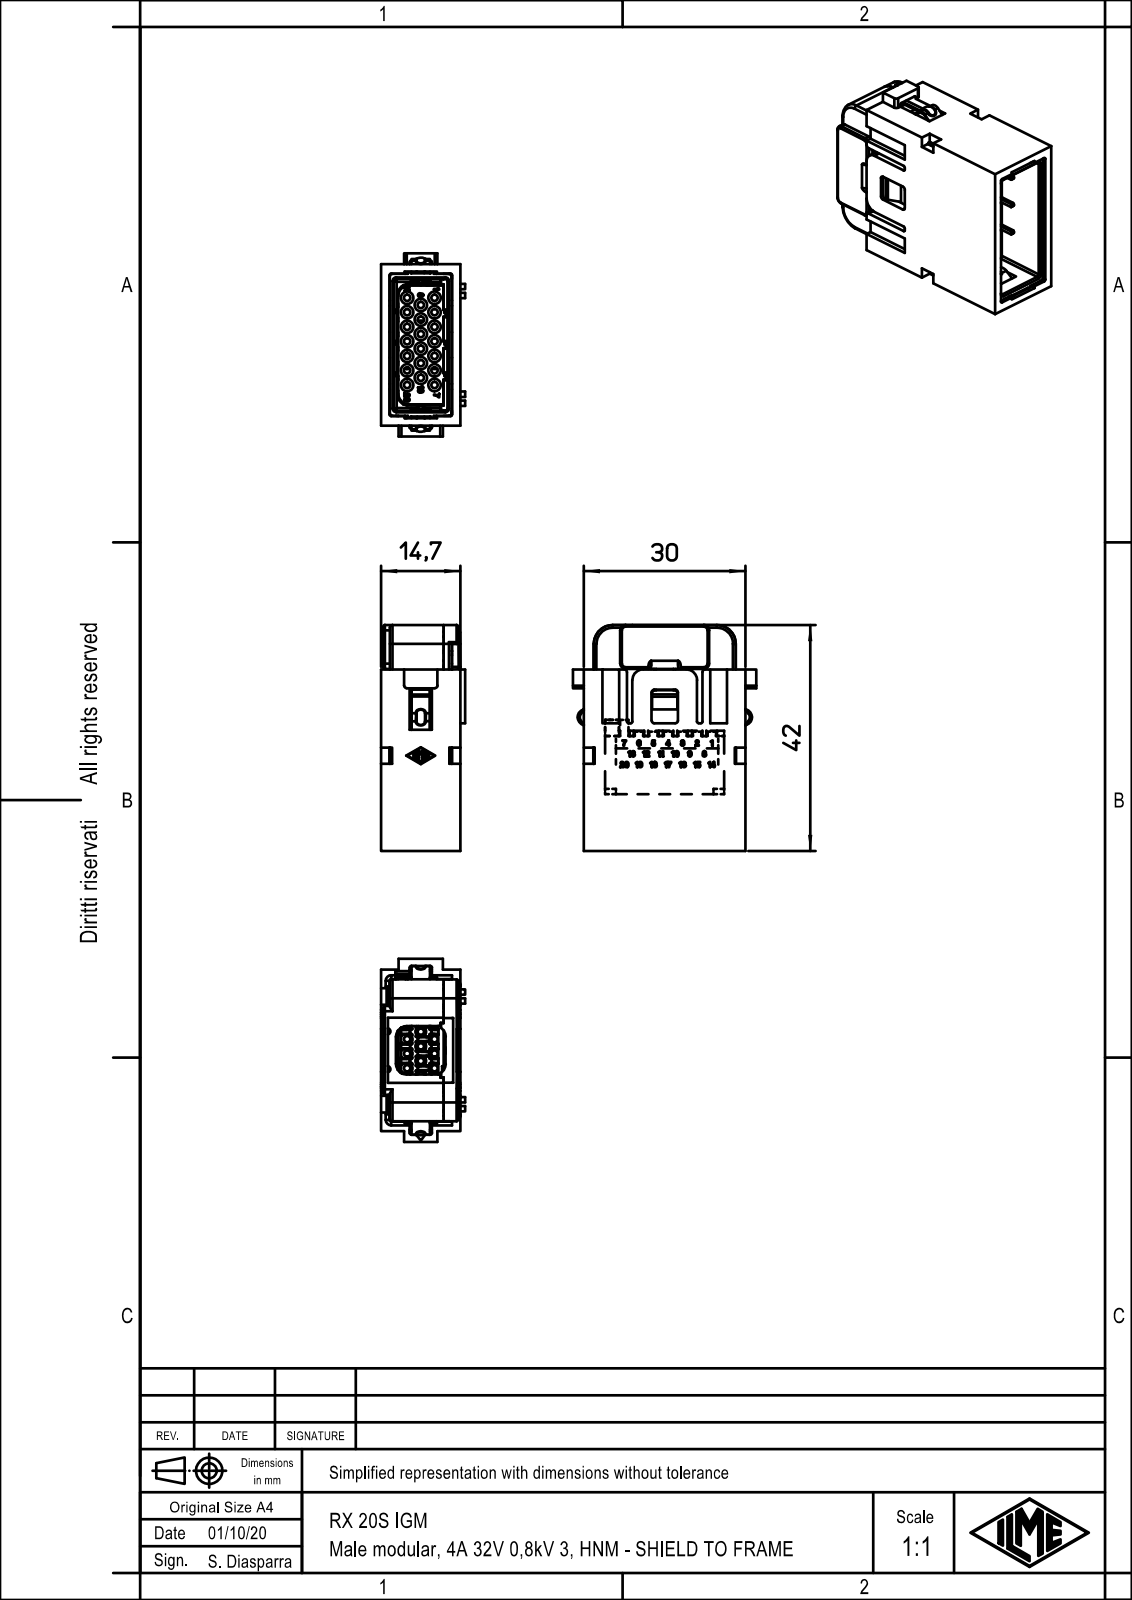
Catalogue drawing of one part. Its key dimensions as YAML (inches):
part_name: "CX_20S_IGM"
step_written_by: "Creo Elements/Direct Modeling 20.1B 02-Apr-2019 (C) Parametric Technology GmbH (AUTOMOTIVE_DESIGN)"
units: inches
bodies: {solids: 1, faces: 439, planar: 289, cylindrical: 108, other: 42}
overall_size: [1.652, 1.339, 0.614]
volume: 0.682
surface_area: 13.63
round_holes:
  - {diameter: 0.039, count: 20}
  - {diameter: 0.197, count: 2}
round_bosses_or_shafts:
  - {diameter: 0.185, count: 2}
partial_cylinders:
  - {radius: 0.012, count: 21}
  - {radius: 0.02, count: 11}
  - {radius: 0.039, count: 6}
  - {radius: 0.016, count: 2}
  - {radius: 0.045, count: 2}
  - {radius: 0.053, count: 2}
  - {radius: 0.059, count: 2}
  - {radius: 0.071, count: 2}
face_to_face_distances: [0.579, 0.122, 0.457, 0.094, 0.484, 0.028, 0.362, 1.181, 0.394, 0.516]
hole_center_spacings: [0.114, 0.189, 0.106, 0.284, 0.213, 0.227, 0.385, 0.319]
